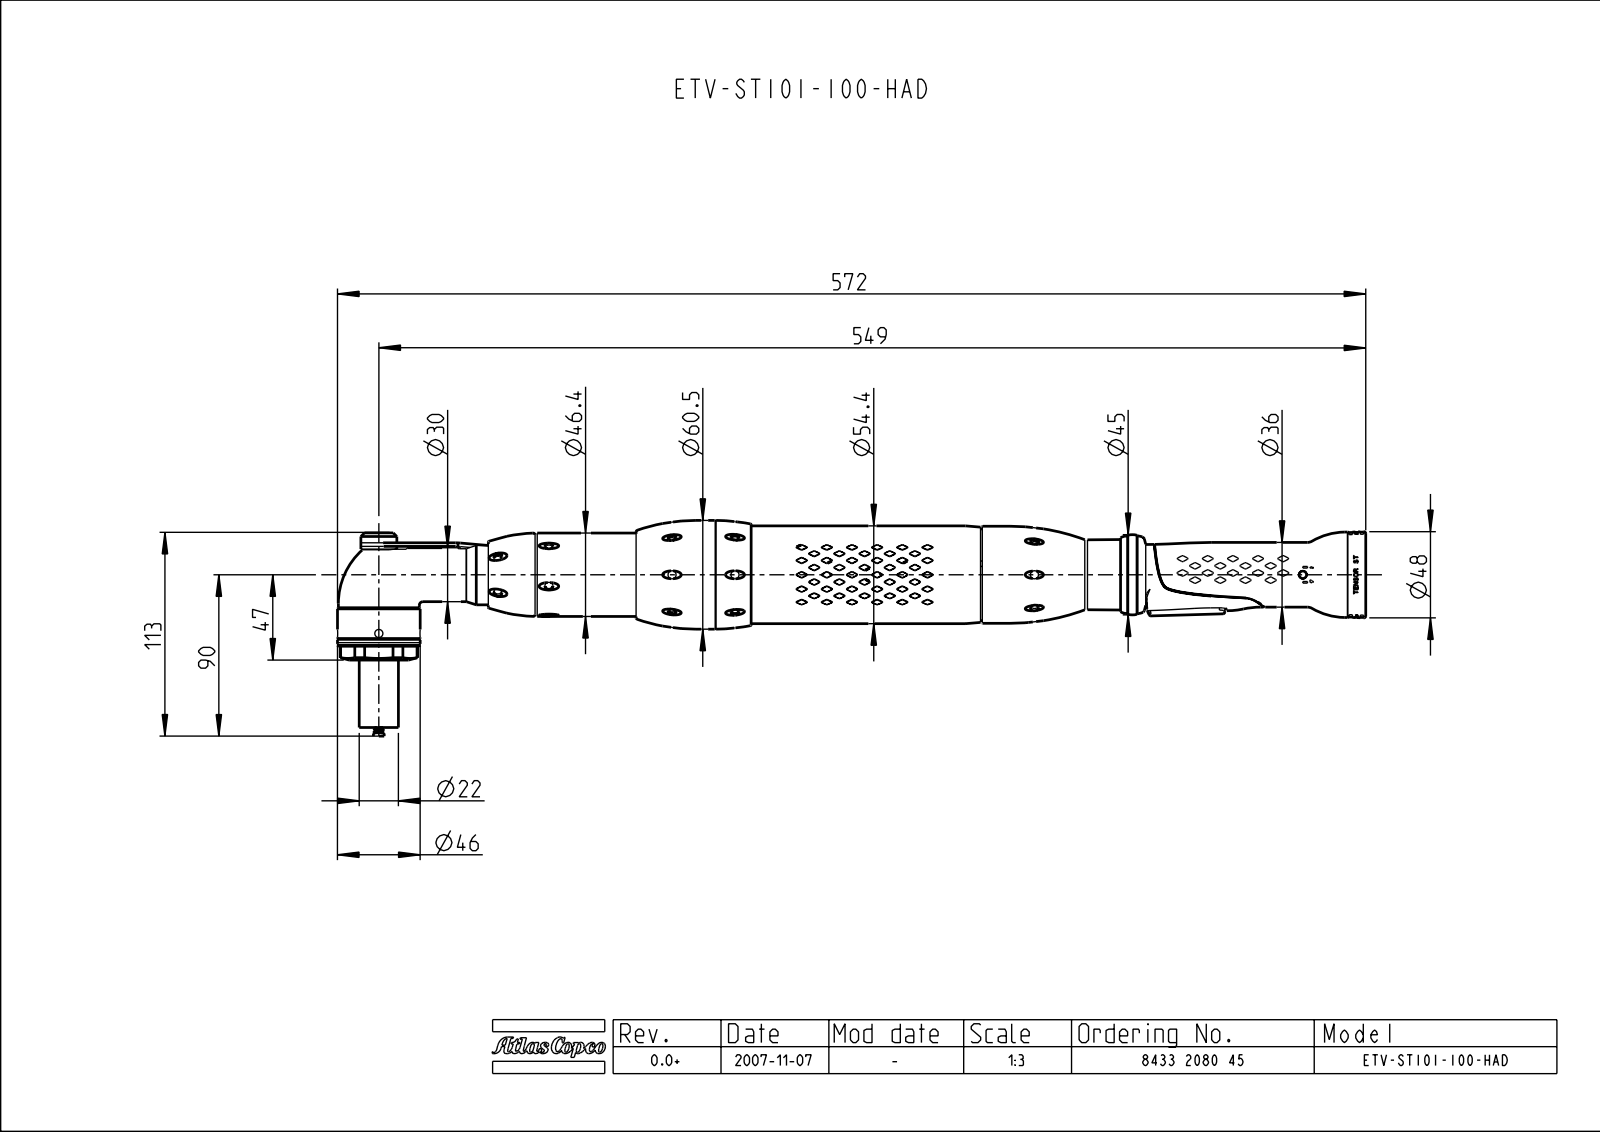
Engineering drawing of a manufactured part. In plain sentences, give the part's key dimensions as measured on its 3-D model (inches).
The part is named "ETV-ST101-100-HAD_SW". Its 3-D file was written by "PRO/ENGINEER BY PARAMETRIC TECHNOLOGY CORPORATION, 2007090 (CONFIG_CONTROL_DESIGN)". It is 0 solids with 649 faces: 70 planar, 242 cylindrical and 337 other. Overall it measures 22.52 by 4.725 by 2.382 inches. Round holes: 15 of diameter 0.177, 1 of diameter 0.65, 1 of diameter 0.748, 1 of diameter 1.433. Round bosses or shafts: 2 of diameter 1.811, 2 of diameter 0.787, 1 of diameter 2.382, 1 of diameter 2.283, 1 of diameter 2.142, 1 of diameter 2.126, 1 of diameter 2.071, 1 of diameter 2.008. Partial cylindrical surfaces (rounded edges, fillets, slot ends): 7 of radius 0.089, 6 of radius 0.079, 4 of radius 0.059, 2 of radius 0.018, 1 of radius 0.02, 1 of radius 0.701, 1 of radius 0.787, 1 of radius 0.846. The main face-to-face distances are 0.079, 0.913, 2.49, 2.569, 0.303, 2.187, 2.265, 0.815, 1.575, 0.098. The hole center spacings are 1.378, 6.559, 7.937, 6.559, 6.559, 7.937, 7.937, 1.377.
